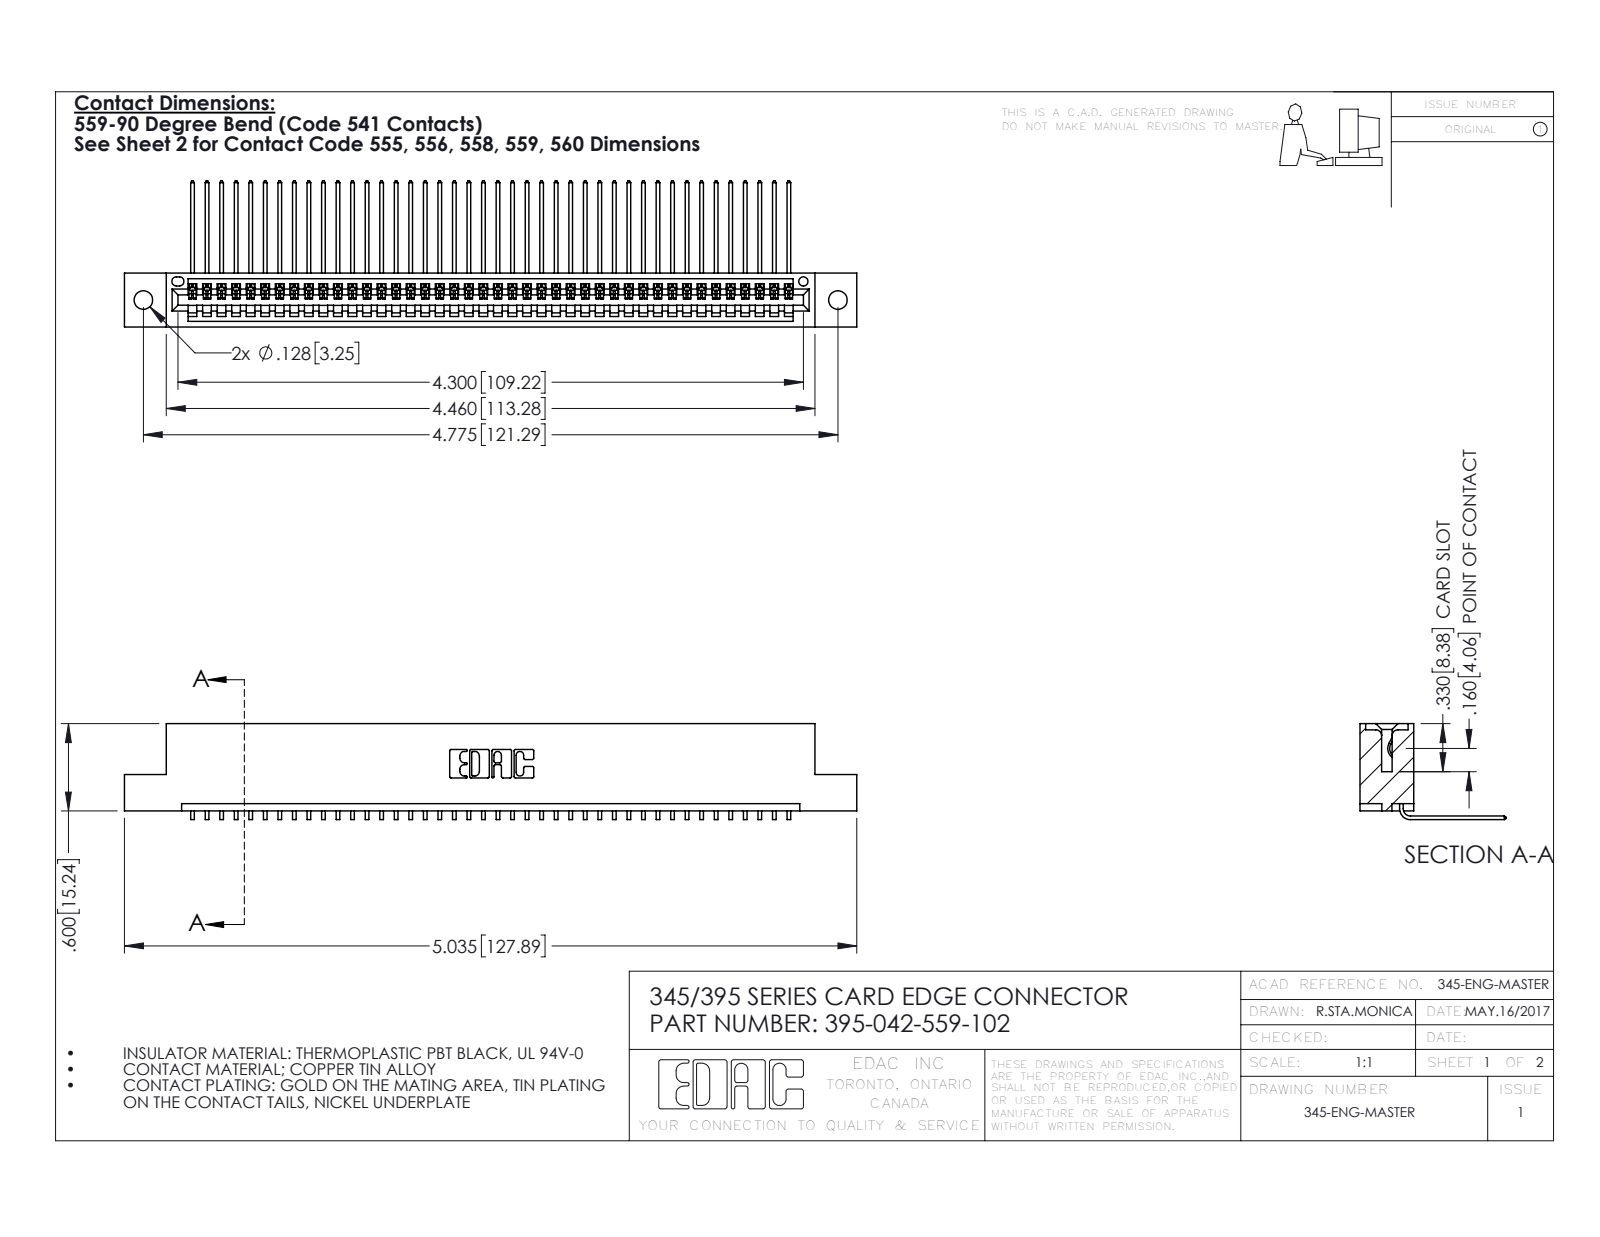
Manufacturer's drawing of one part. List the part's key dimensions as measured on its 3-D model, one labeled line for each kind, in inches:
Part name (STEP PRODUCT): 395-042-559-102; 345-292-001_558 559 Tail - 1; 345 Part_Flush Mounting Lugs - 0.128 Dia
STEP written by: SolidWorks 2016 (CONFIG_CONTROL_DESIGN)
Units: inches
Bodies: 43 solids, 2646 faces (1844 planar, 802 cylindrical, 0 other)
Overall size (bounding box): 5.035 × 1.005 × 0.659
Volume: 0.748 in³ · Surface area: 26.09 in²
Round holes (diameter × count): ⌀0.128 ×2, ⌀0.064 ×1
Partial cylindrical surfaces — rounded edges, fillets, slot ends (radius × count): R0.006 ×84, R0.01 ×22, R0.007 ×6, R0.031 ×6, R0.026 ×3, R0.031 ×2, R0.04 ×2, R0.014 ×1
Main face-to-face distances: 0.298, 0.072, 0.37, 0.2, 0.098, 0.272, 0.025, 0.225, 0.149, 0.072
Hole centre spacings: 0.27, 4.539, 4.775
